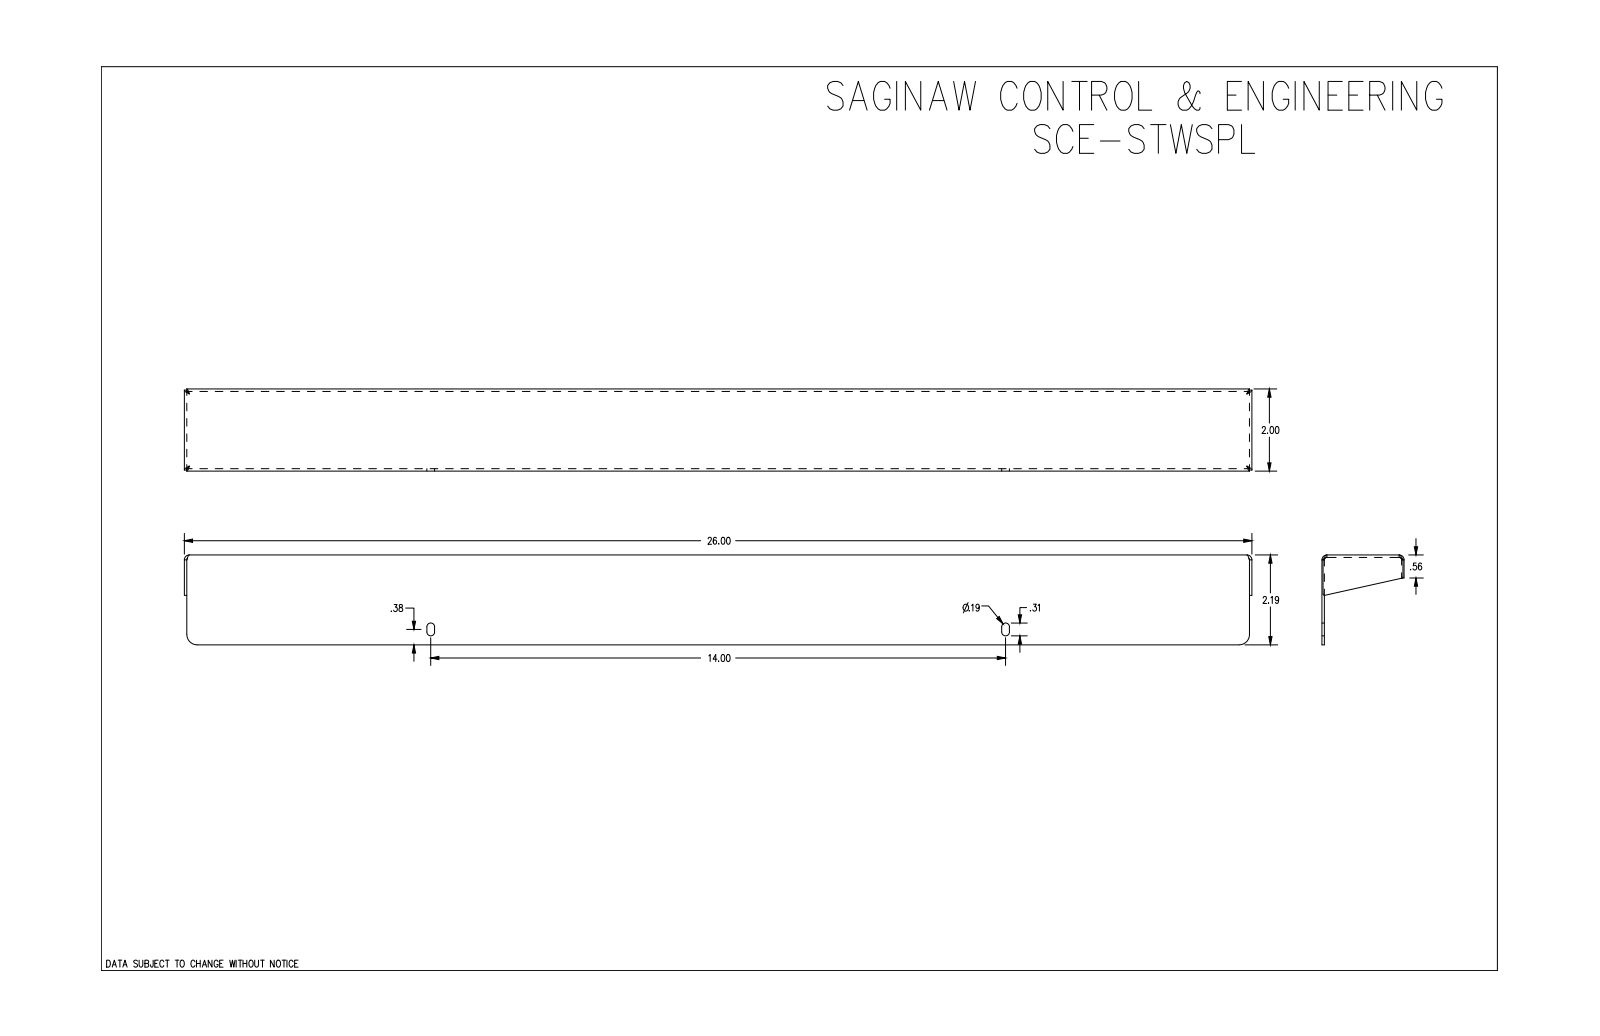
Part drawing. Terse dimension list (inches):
name: SCE-STWSPL
written by: SolidWorks 2021 (AUTOMOTIVE_DESIGN)
unit: in
bodies: 5 solids, 252 faces (158 planar, 28 cylindrical, 66 other)
size: 26 × 2.188 × 2.145
volume: 7.315 in³; area: 247.7 in²
holes: 2× ⌀0.164
bosses: 2× ⌀0.358, 2× ⌀0.185
rounds: 8× R0.03, 4× R0.058, 4× R0.094, 4× R0.118, 2× R0.236
face distances: 0.06, 1.94, 1.88, 2, 25.94, 2.128, 2.187, 26, 25.88, 0.344
hole spacings: 14
